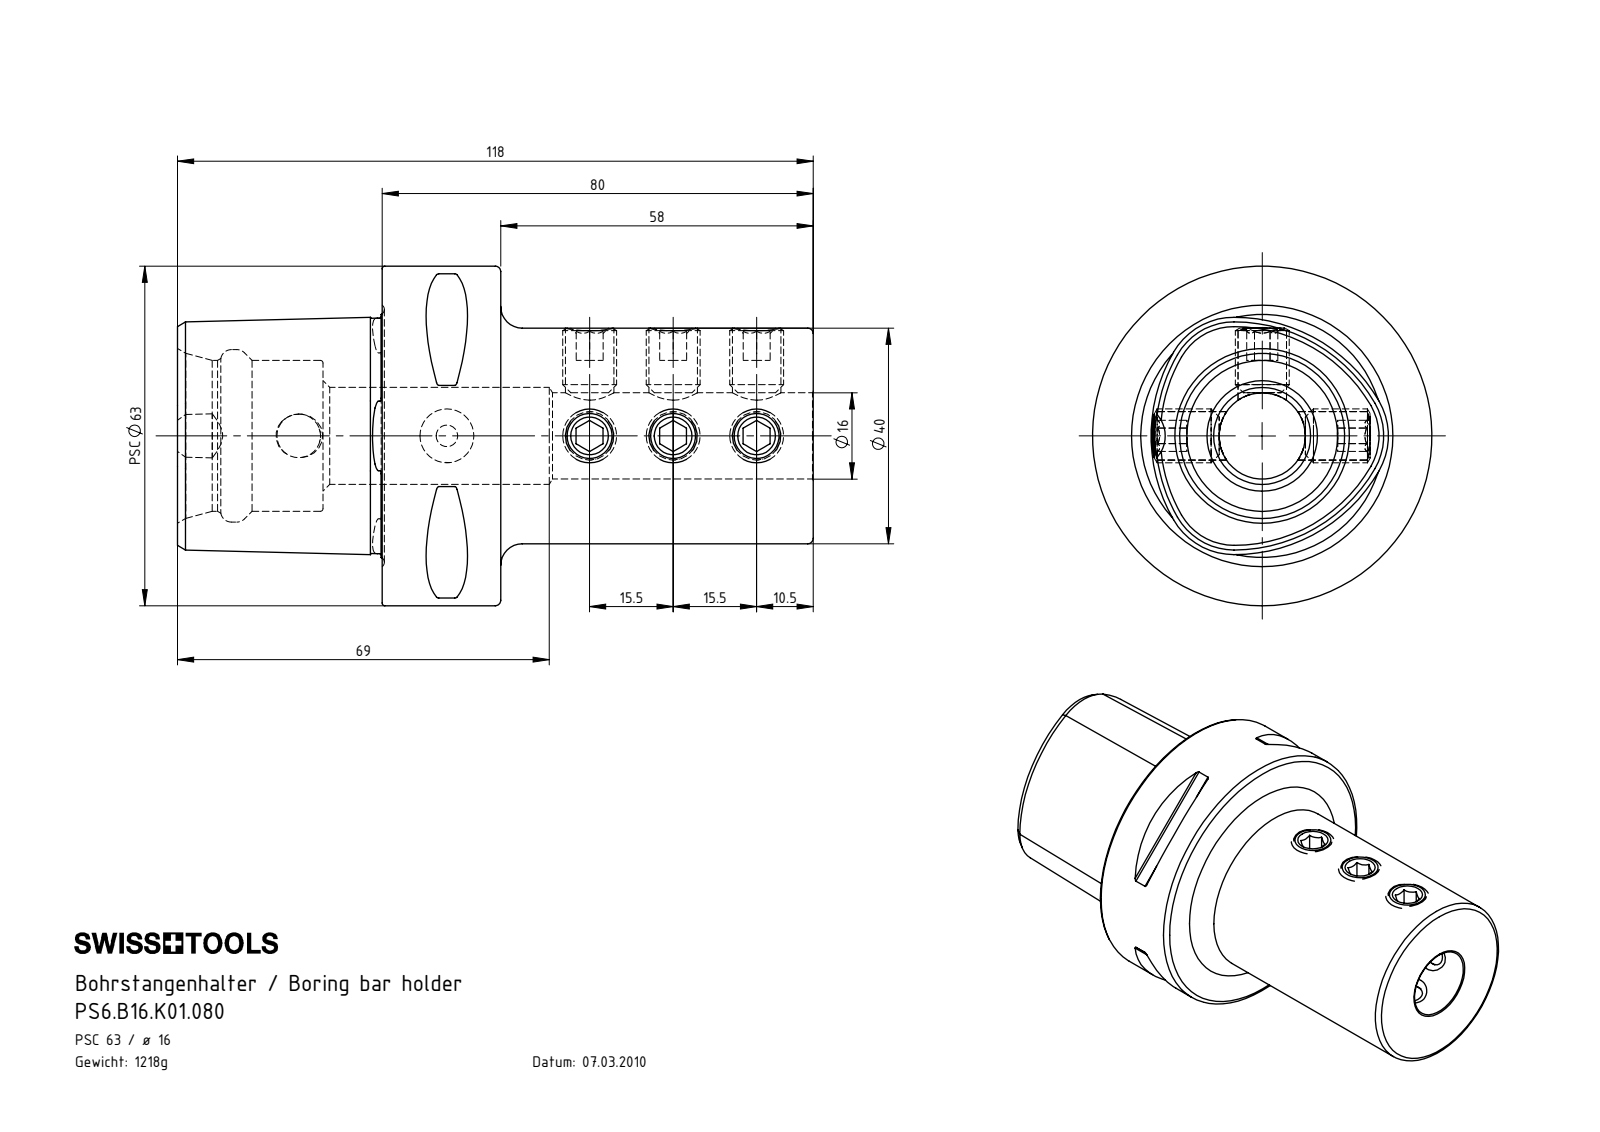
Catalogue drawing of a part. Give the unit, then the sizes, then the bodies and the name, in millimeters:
Units: millimetres
Overall size (bounding box): 118 × 63 × 63
Round holes (diameter × count): ⌀9 ×6, ⌀4 ×1, ⌀8.1 ×1, ⌀16 ×1, ⌀18 ×1, ⌀28 ×1, ⌀32 ×1
Round bosses / shafts (diameter × count): ⌀10 ×6, ⌀63 ×1, ⌀40 ×1
Partial cylindrical surfaces — rounded edges, fillets, slot ends (radius × count): R0.5 ×8, R6 ×1
Main face-to-face distances: 22, 80, 58, 38, 60, 118, 5, 15.5, 7.75, 6
Hole centre spacings: 15.5, 31, 26.5, 27.5, 42, 54, 57.5, 69.5
Volume: 155 554 mm³ · Surface area: 37 065 mm²
Bodies: 10 solids, 299 faces (101 planar, 65 cylindrical, 133 other)
Part name (STEP PRODUCT): PS6-B16.K01.080_A; PS6.B16.K01.080; ISO 4026 - M10 x 12_PreviewCfg
STEP written by: SolidWorks 2017 (AUTOMOTIVE_DESIGN)
